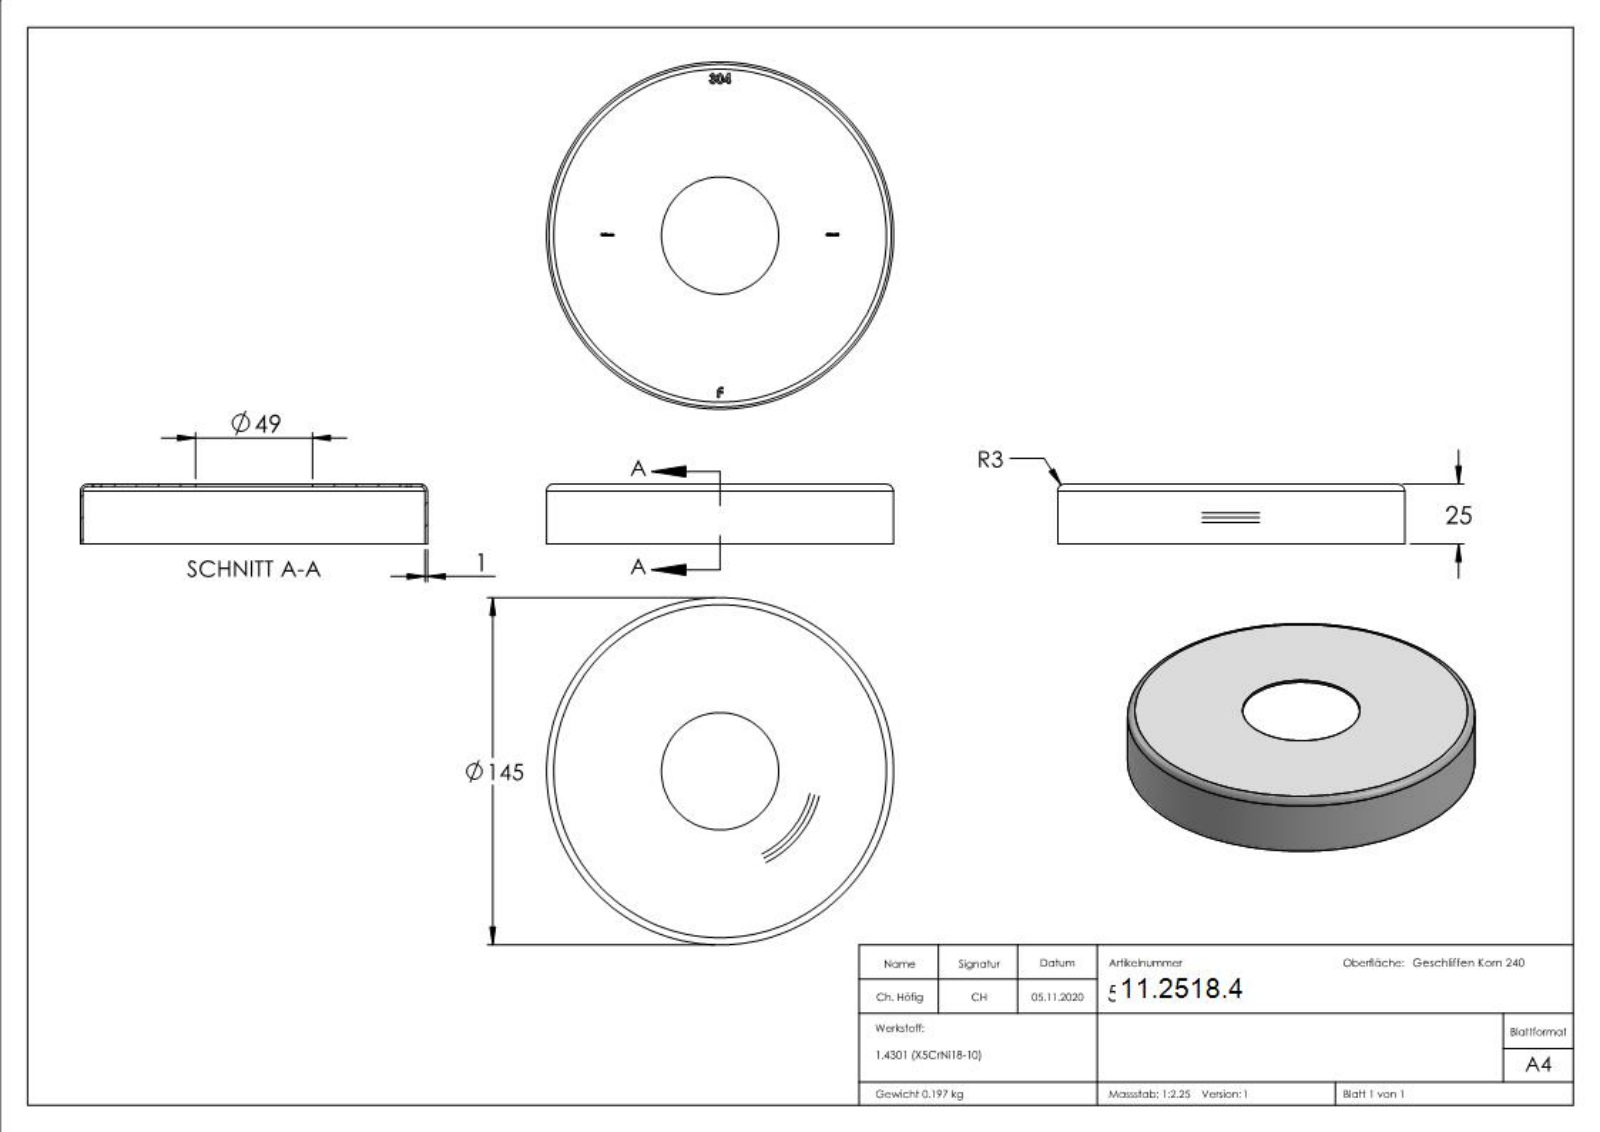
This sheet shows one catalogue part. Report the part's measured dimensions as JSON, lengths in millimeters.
{"part_name": "50846-240", "step_written_by": "SolidWorks 2018 (CONFIG_CONTROL_DESIGN)", "units": "millimeters", "bodies": {"solids": 1, "faces": 303, "planar": 162, "cylindrical": 6, "other": 135}, "overall_size": [145, 145, 25], "volume_mm3": 24994, "surface_area_mm2": 50613, "round_holes": [[49, 1], [143, 1]], "round_bosses_or_shafts": [[145, 1]], "face_to_face_distances": [1, 24, 25, 24.1, 0.9, 0.71, 5, 4.29, 0.58, 0.69]}
